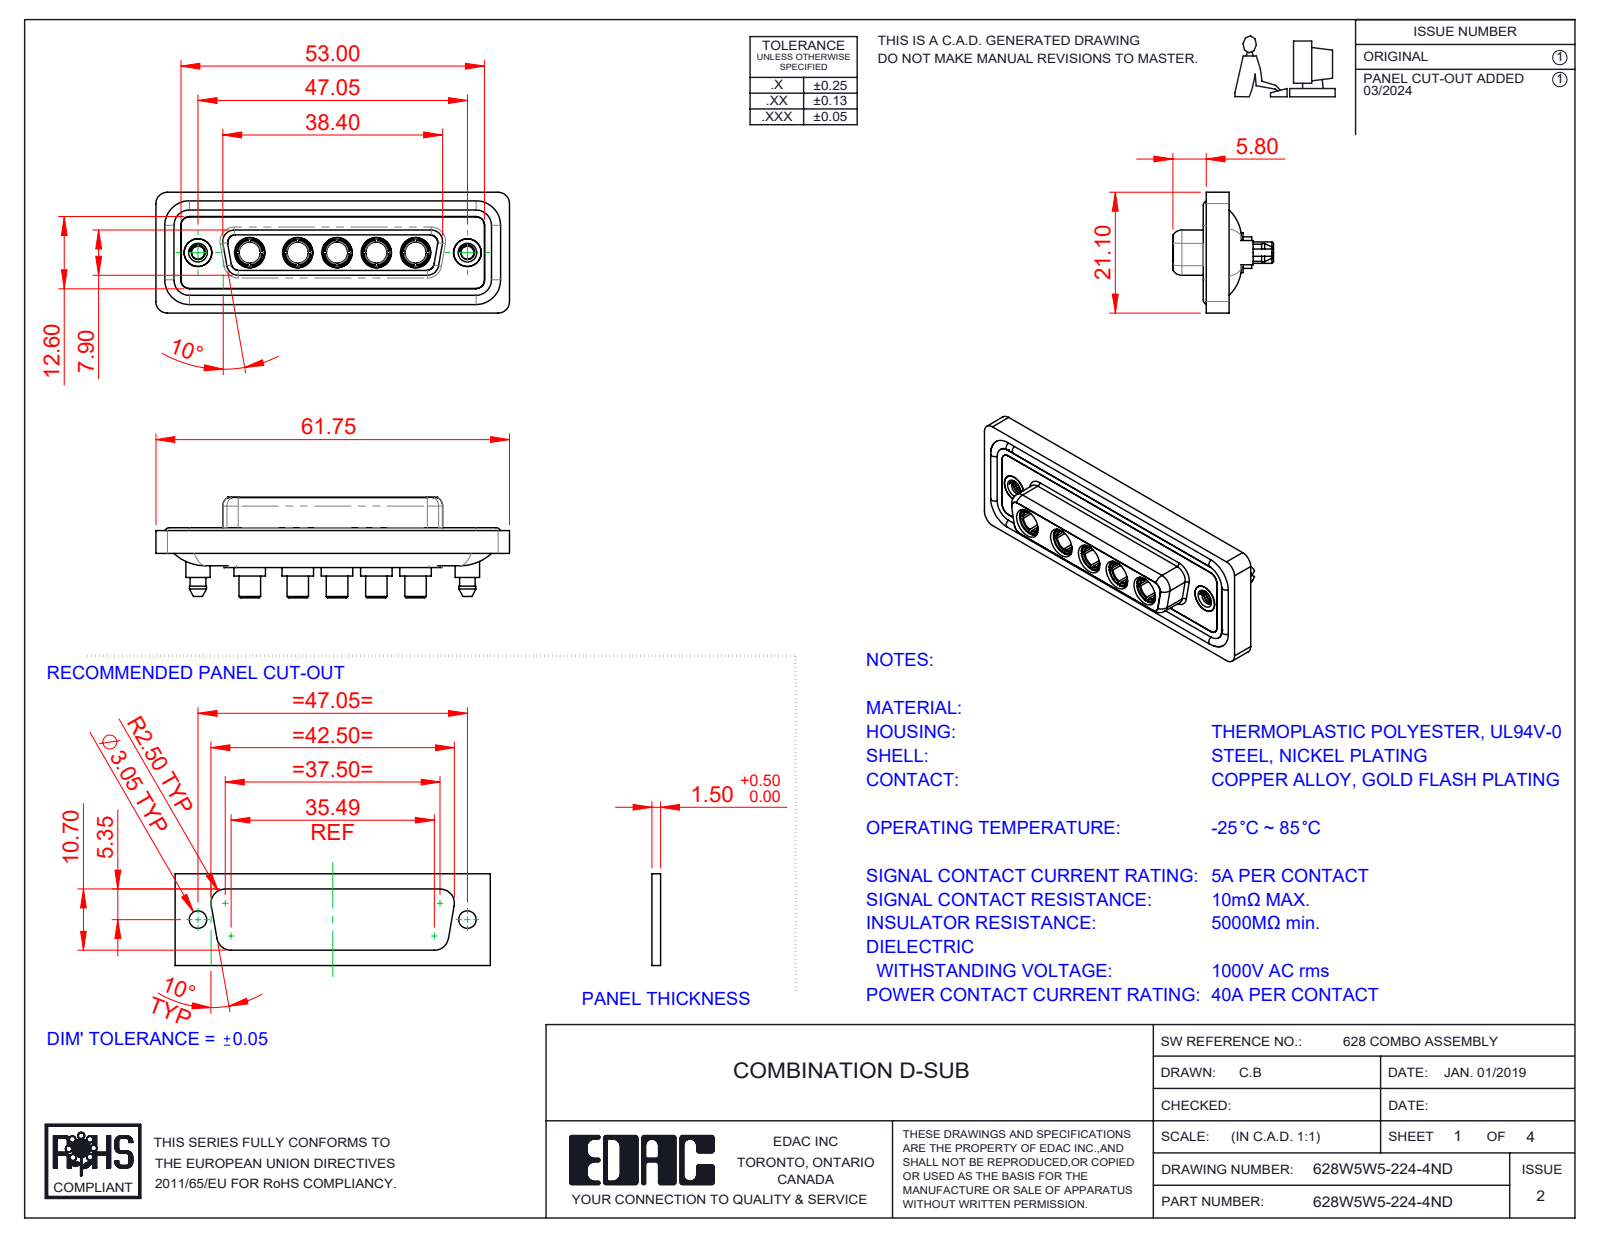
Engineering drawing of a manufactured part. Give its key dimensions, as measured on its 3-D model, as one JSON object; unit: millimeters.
{"part_name": "Power Socket_40A S; 628Combo Shell Front_25 Contacts; 628Combo Housing_5W5; 628Combo Threaded Boardlock_D (+3 more)", "step_written_by": "SolidWorks 2023 (CONFIG_CONTROL_DESIGN)", "units": "millimeters", "bodies": {"solids": 17, "faces": 822, "planar": 266, "cylindrical": 351, "other": 205}, "overall_size": [61.75, 21.1, 17.55], "volume_mm3": 8400, "surface_area_mm2": 13809, "round_holes": [[4.85, 7], [3.7, 5], [5.3, 5], [2.26, 2], [4, 2], [4.05, 2], [5, 2]], "round_bosses_or_shafts": [[5.5, 5], [5.2, 5], [4.96, 5], [4.75, 5], [3.75, 5], [1.6, 4], [5.4, 2], [4.95, 2]], "partial_cylinders_radius": [[1.5, 24], [2, 18], [1.6, 10], [1.35, 8], [2.1, 5], [0.25, 4], [0.5, 4], [0.6, 4]], "face_to_face_distances": [0.4, 1.8, 7.45, 5.65, 0.5, 7.05, 6.6, 1.6, 1.1, 2.9], "hole_center_spacings": [6.86, 9.04, 13.72, 38.01, 8.39, 15.25, 15.9, 17.43]}
